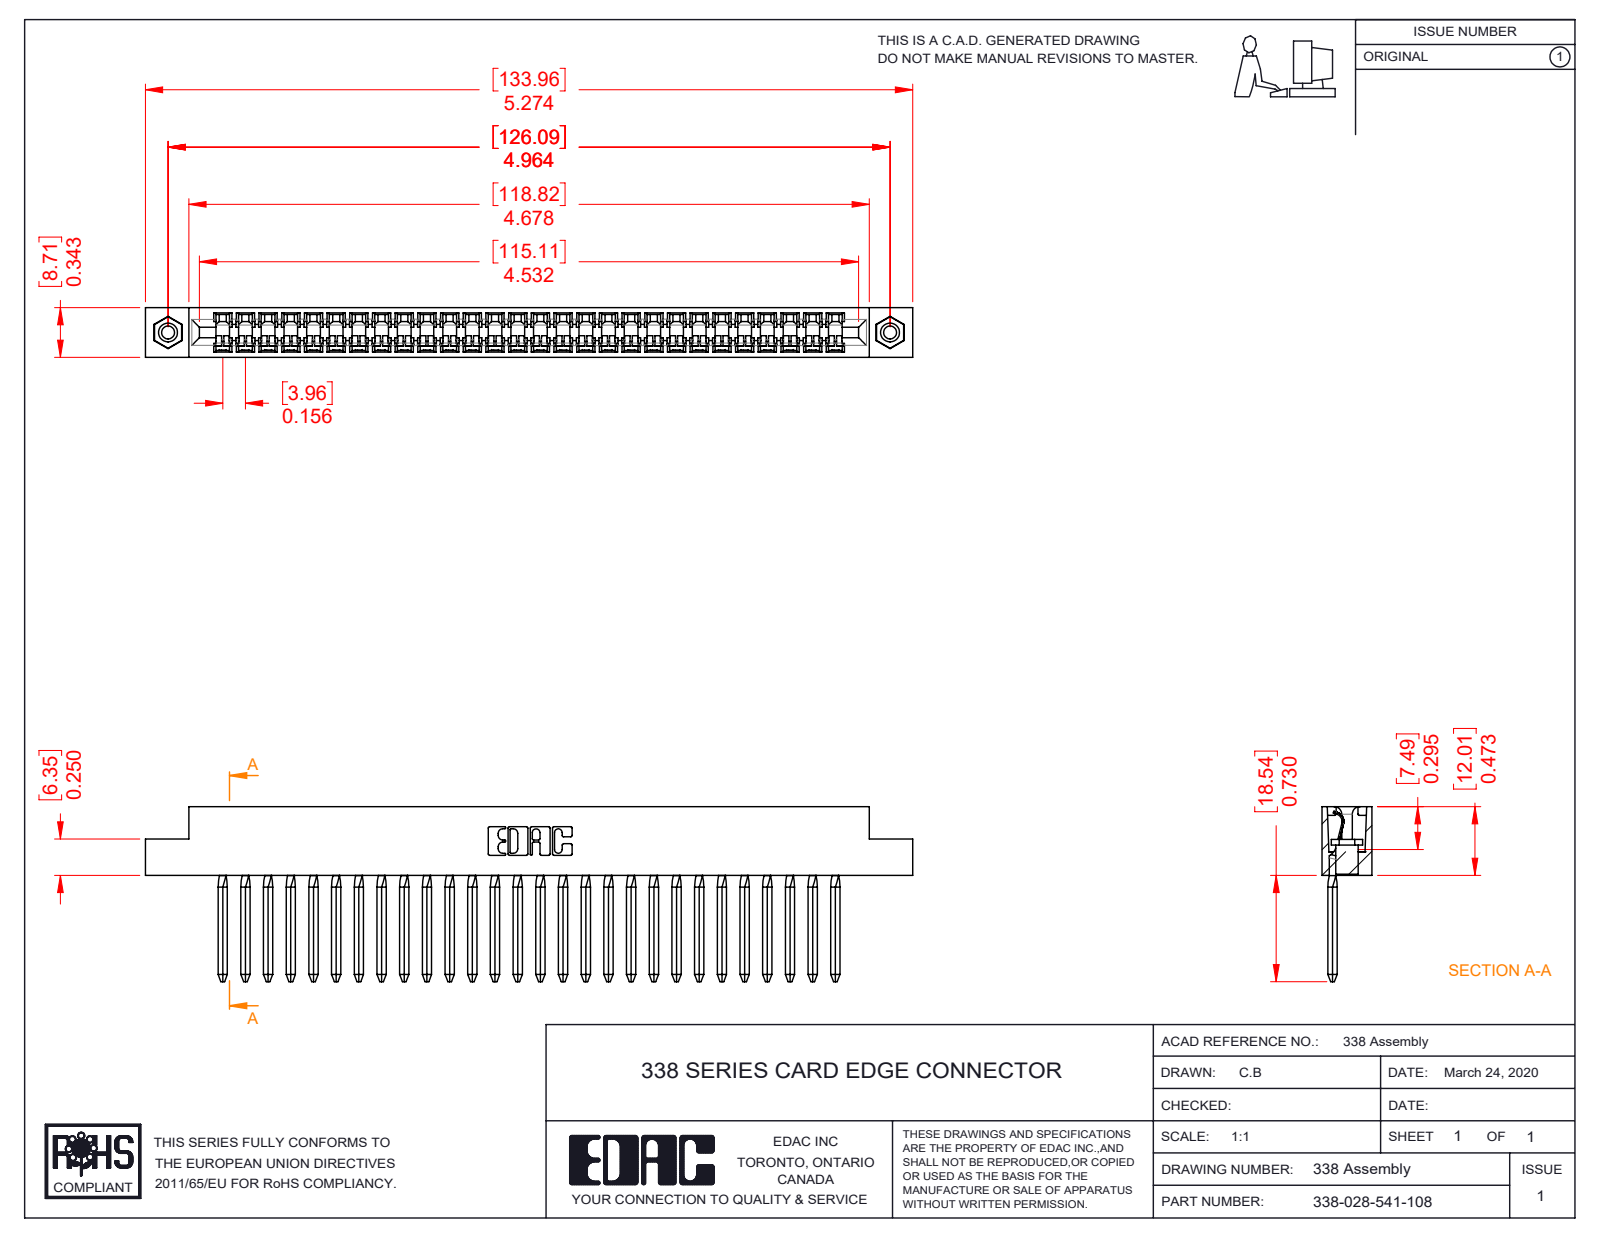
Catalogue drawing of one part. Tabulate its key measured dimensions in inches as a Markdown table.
| quantity | value |
| --- | --- |
| part name | 345-250-001_345-250-003-102; 338-290-001_541; 338-210-001_338-210-028-004; 338-028-541-108 |
| STEP written by | SolidWorks 2016 (CONFIG_CONTROL_DESIGN) |
| units | inches |
| bodies | 31 solids, 2758 faces (1902 planar, 728 cylindrical, 128 other) |
| overall size | 5.274 × 1.203 × 0.343 |
| volume | 0.573 in³ |
| surface area | 23.89 in² |
| round holes (diameter × count) | 0.089 × 2, 0.125 × 2, 0.156 × 2 |
| round bosses / shafts (diameter × count) | 0.155 × 2 |
| partial cylindrical surfaces (radius × count) | 0.025 × 114, 0.008 × 28, 0.055 × 23, 0.067 × 23, 0.01 × 22, 0.1 × 22, 0.007 × 6, 0.031 × 6 |
| main face-to-face distances | 0.343, 0.156, 0.11, 0.207, 0.135, 0.624, 0.78, 0.468, 0.048, 0.295 |
| hole center spacings | 4.964 |
